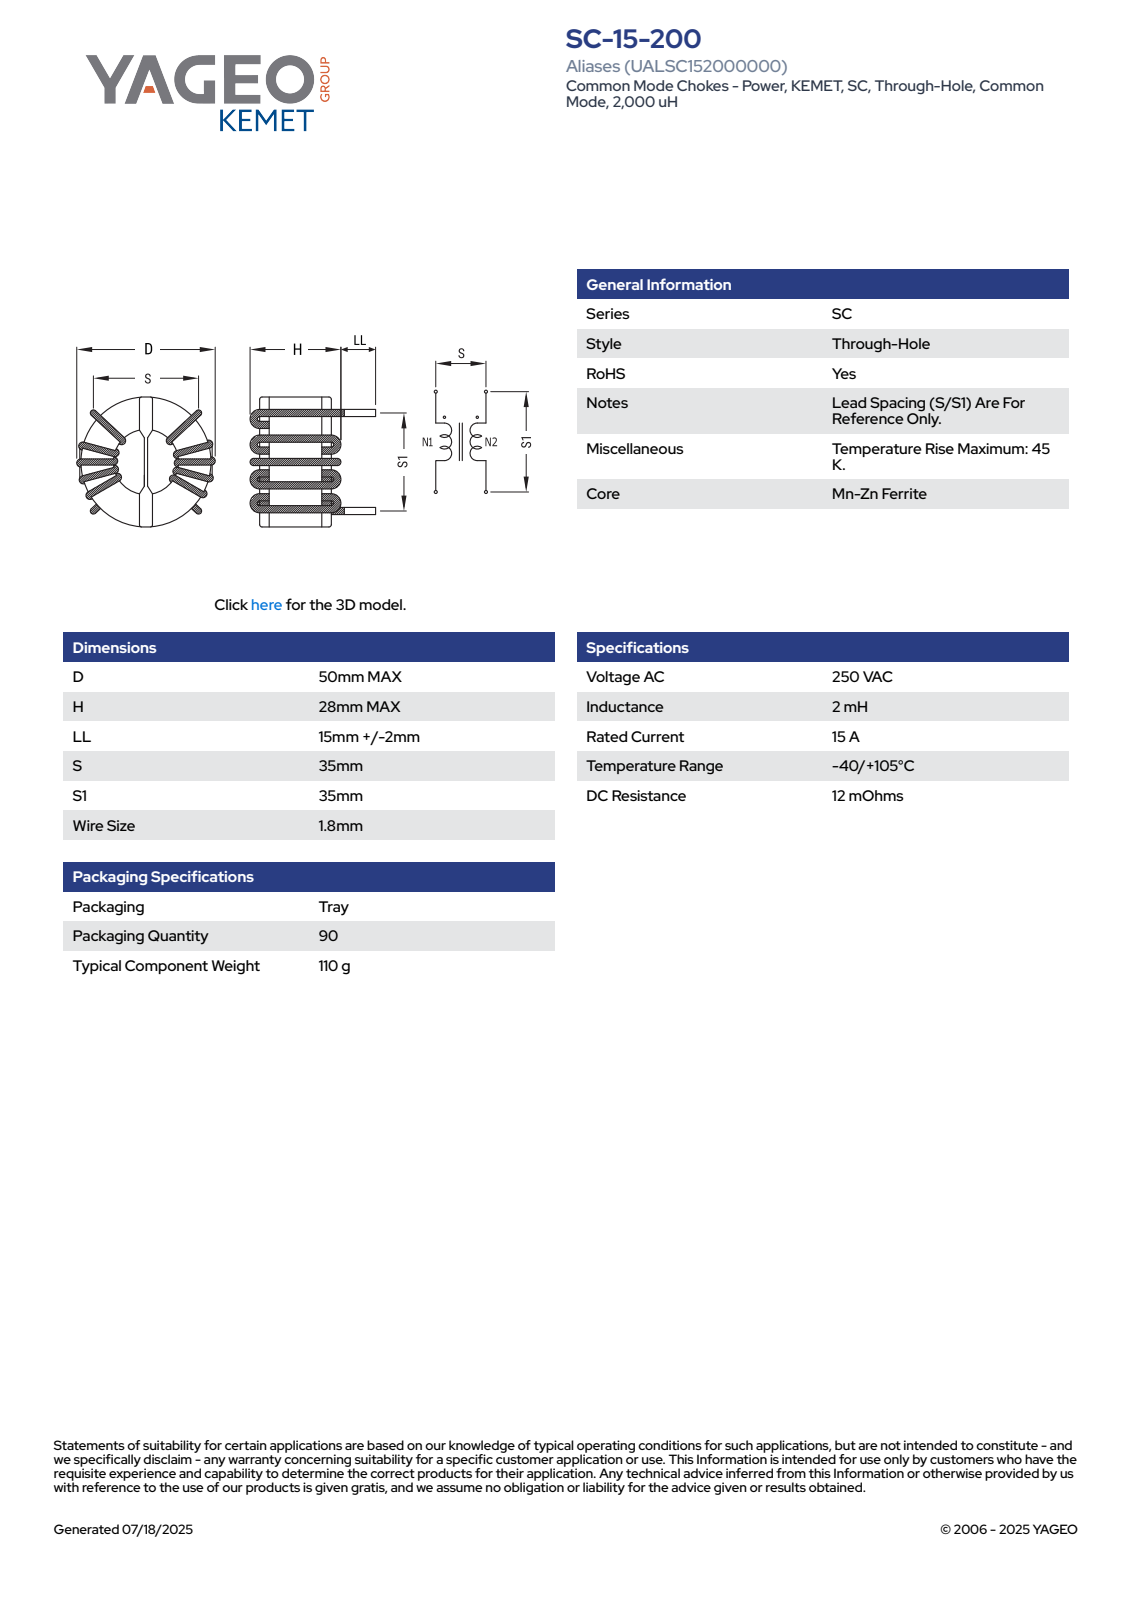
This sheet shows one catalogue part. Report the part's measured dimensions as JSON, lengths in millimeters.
{"part_name": "SC-15-200", "step_written_by": "SolidWorks 2018 (AUTOMOTIVE_DESIGN)", "units": "millimeters", "bodies": {"solids": 1, "faces": 369, "planar": 131, "cylindrical": 121, "other": 117}, "overall_size": [50, 45.73, 43], "volume_mm3": 38225, "surface_area_mm2": 12592, "round_holes": [[13.2, 1]], "round_bosses_or_shafts": [[1.8, 8]], "partial_cylinders_radius": [[0.9, 38], [0.2, 10], [0.5, 2], [1.1, 2], [8.65, 1], [9.35, 1], [9.45, 1], [9.5, 1]], "face_to_face_distances": [23.7, 1.2, 2, 0.8, 5.28, 12.8, 3.2, 4, 19.7, 5.6]}
